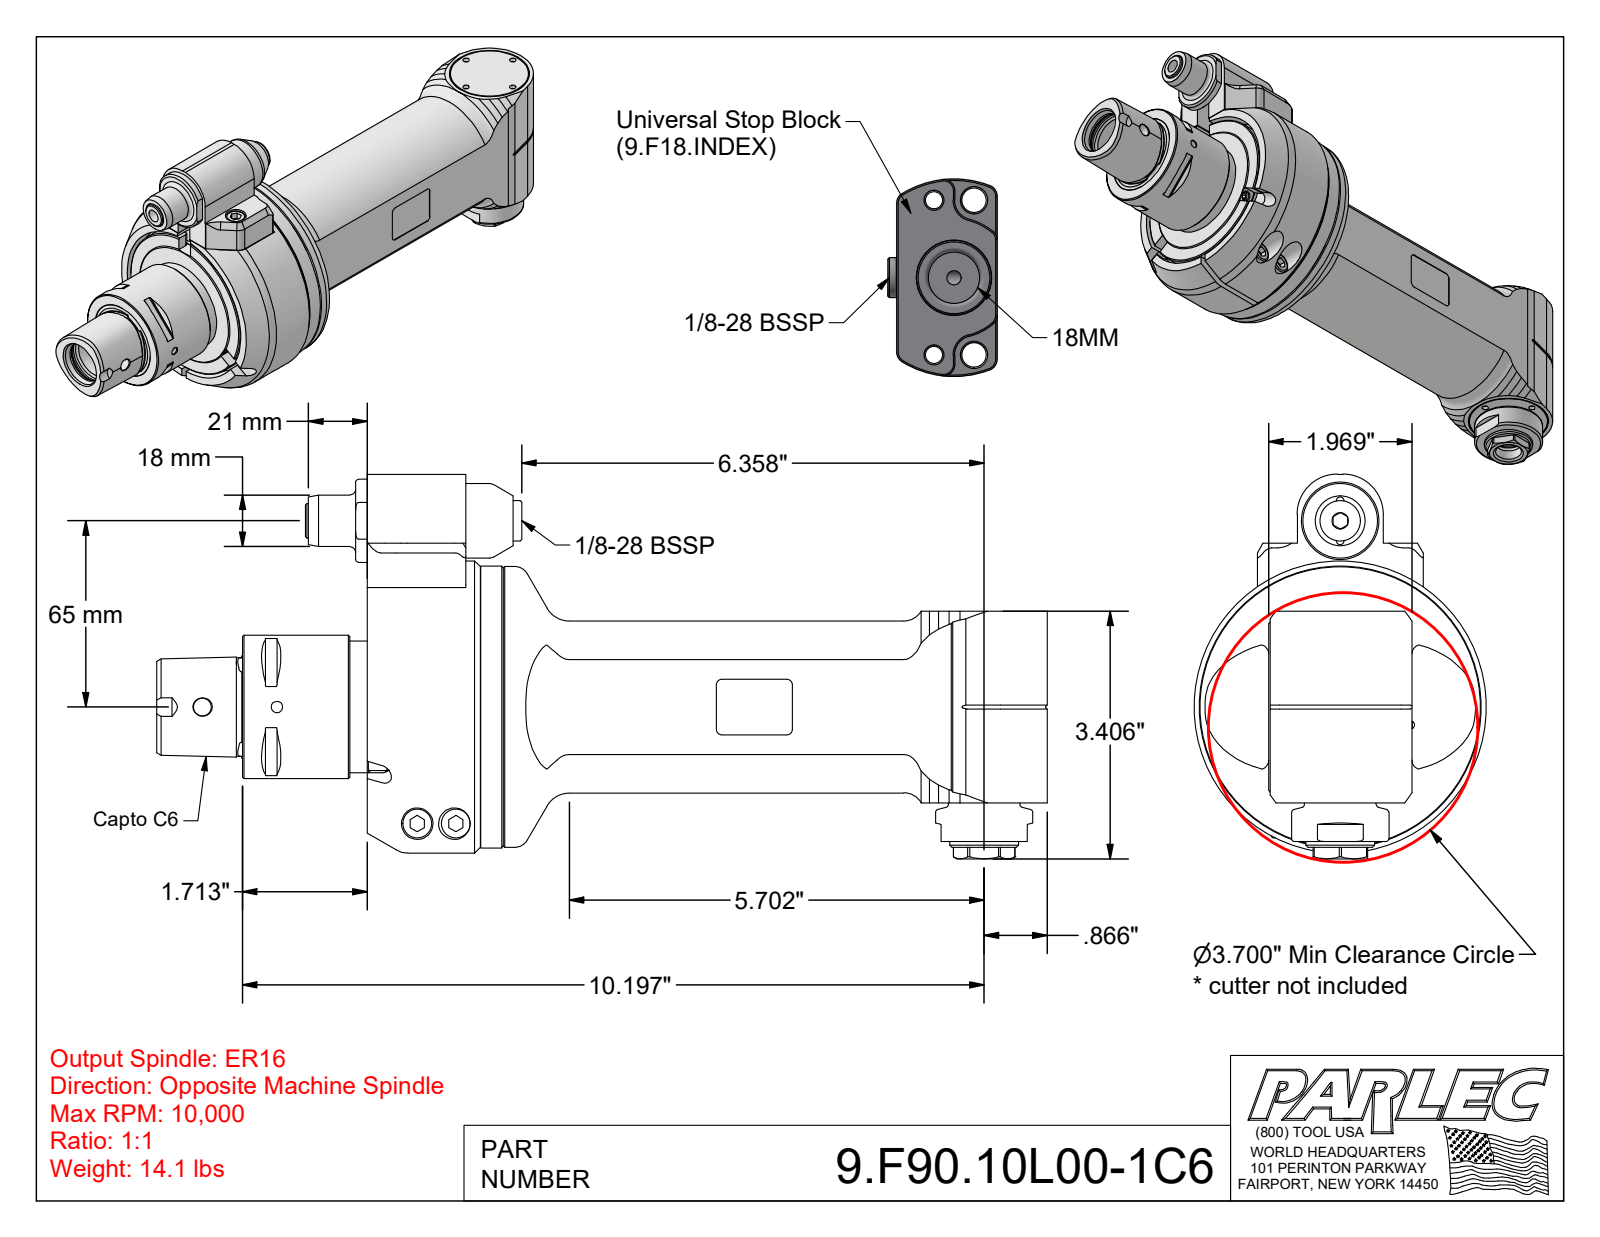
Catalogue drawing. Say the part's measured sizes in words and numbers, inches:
The part is named "9.F90.10L00-1C6; 9_GA1_656_2 (Type 1, Capto C6, 65mm); 9_F90_10L00". Its 3-D file was written by "Autodesk Inventor 2022 (AUTOMOTIVE_DESIGN)". It is 7 solids with 600 faces: 274 planar, 149 cylindrical and 177 other. Overall it measures 12.244 by 5.285 by 4.016 inches. Its volume is 64.73 cubic inches and its surface area 242.6 square inches. Round holes: 20 of diameter 0.335, 4 of diameter 0.126, 3 of diameter 0.433, 2 of diameter 0.102, 2 of diameter 0.165, 2 of diameter 0.197, 2 of diameter 0.409, 1 of diameter 0.098, 1 of diameter 0.118, 1 of diameter 0.157, 1 of diameter 0.24, 1 of diameter 0.256. Round bosses or shafts: 4 of diameter 0.394, 4 of diameter 0.236, 2 of diameter 0.315, 2 of diameter 0.098, 1 of diameter 4.016, 1 of diameter 3.874, 1 of diameter 3.858, 1 of diameter 3.031. Partial cylindrical surfaces (rounded edges, fillets, slot ends): 12 of radius 0.079, 8 of radius 0.012, 5 of radius 0.157, 2 of radius 0.016, 2 of radius 0.02, 2 of radius 0.039, 2 of radius 0.138, 2 of radius 0.197. The main face-to-face distances are 1.26, 1.969, 0.02, 1.555, 0.295, 0.276, 0.335, 1.024, 1.22, 0.197. The hole center spacings are 1.516, 3.002, 1.824, 0.422, 2.144, 2.914, 3.031, 1.233.
